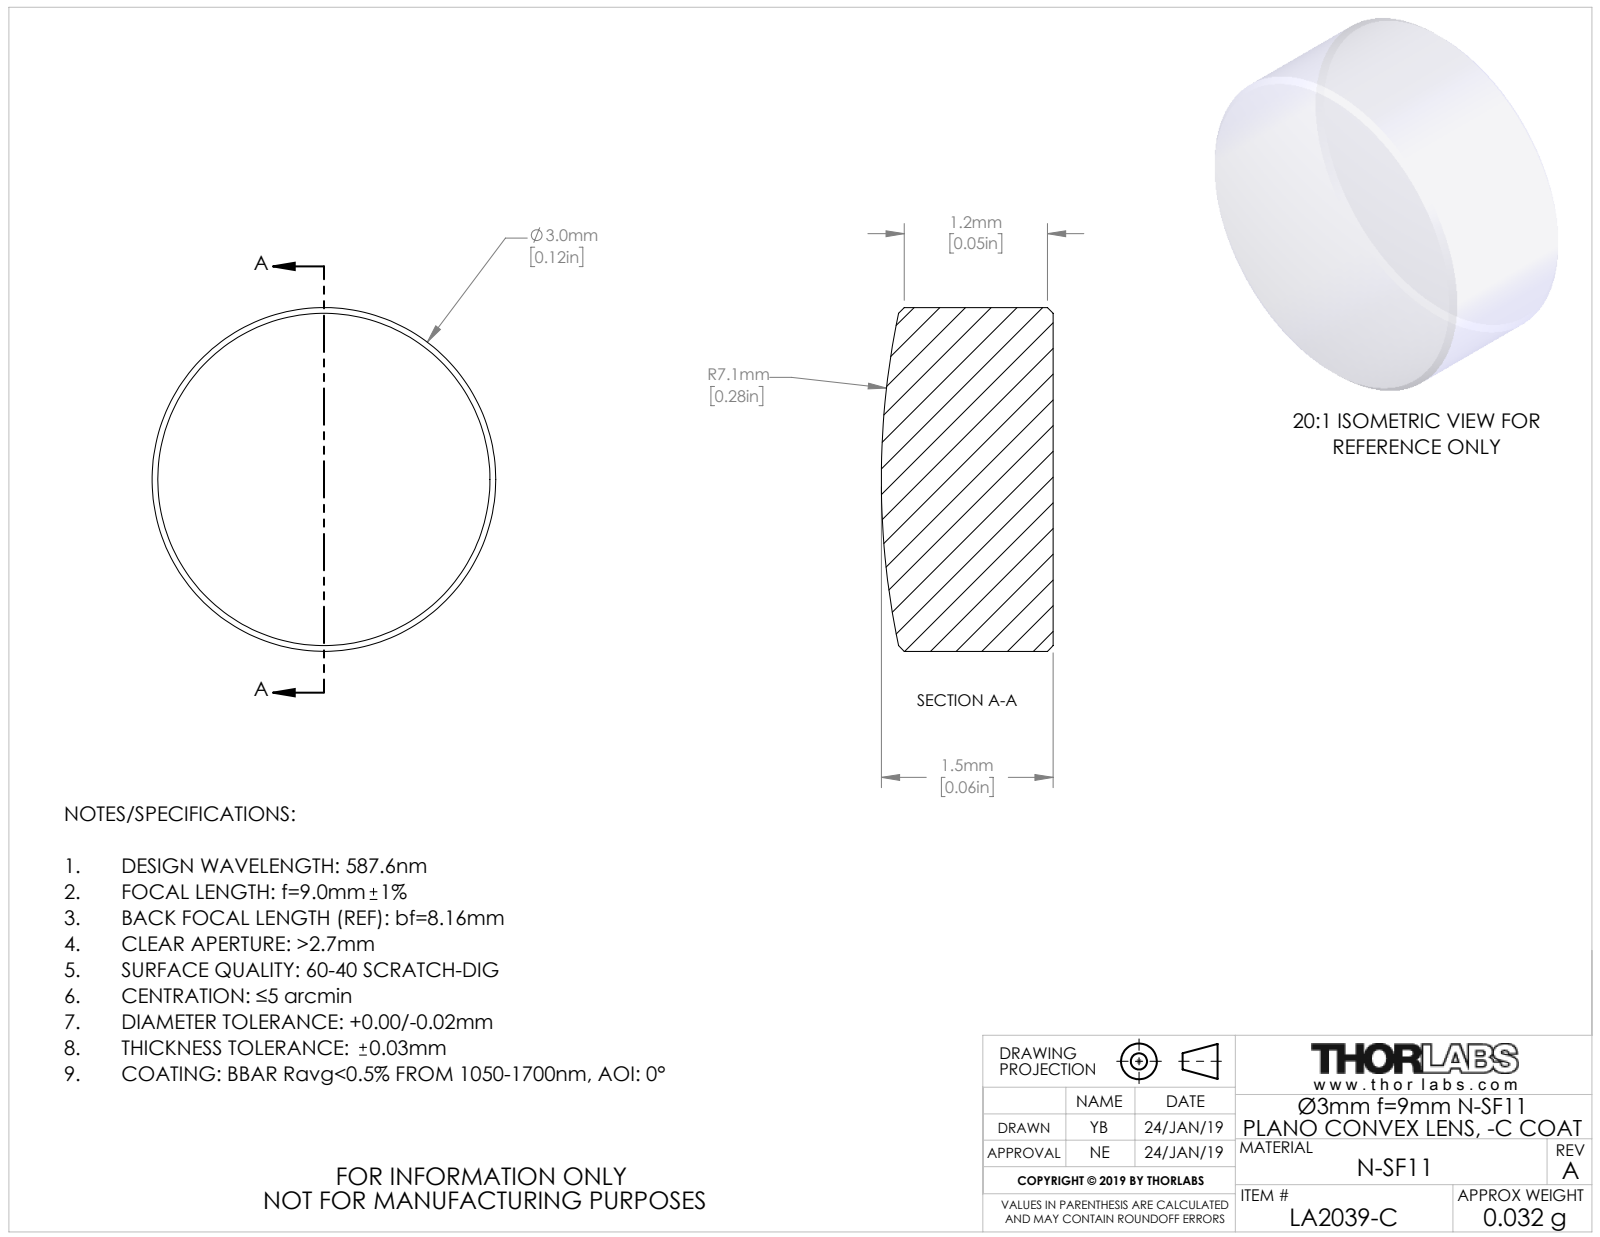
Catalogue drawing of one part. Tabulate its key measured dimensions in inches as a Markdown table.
| quantity | value |
| --- | --- |
| part name | TTN162762-E0W |
| STEP written by | SolidWorks 2018 (CONFIG_CONTROL_DESIGN) |
| units | inches |
| bodies | 1 solid, 9 faces (1 planar, 2 cylindrical, 6 other) |
| overall size | 0.118 × 0.118 × 0.059 |
| volume | 0.001 in³ |
| surface area | 0.04 in² |
| round bosses / shafts (diameter × count) | 0.118 × 1 |
